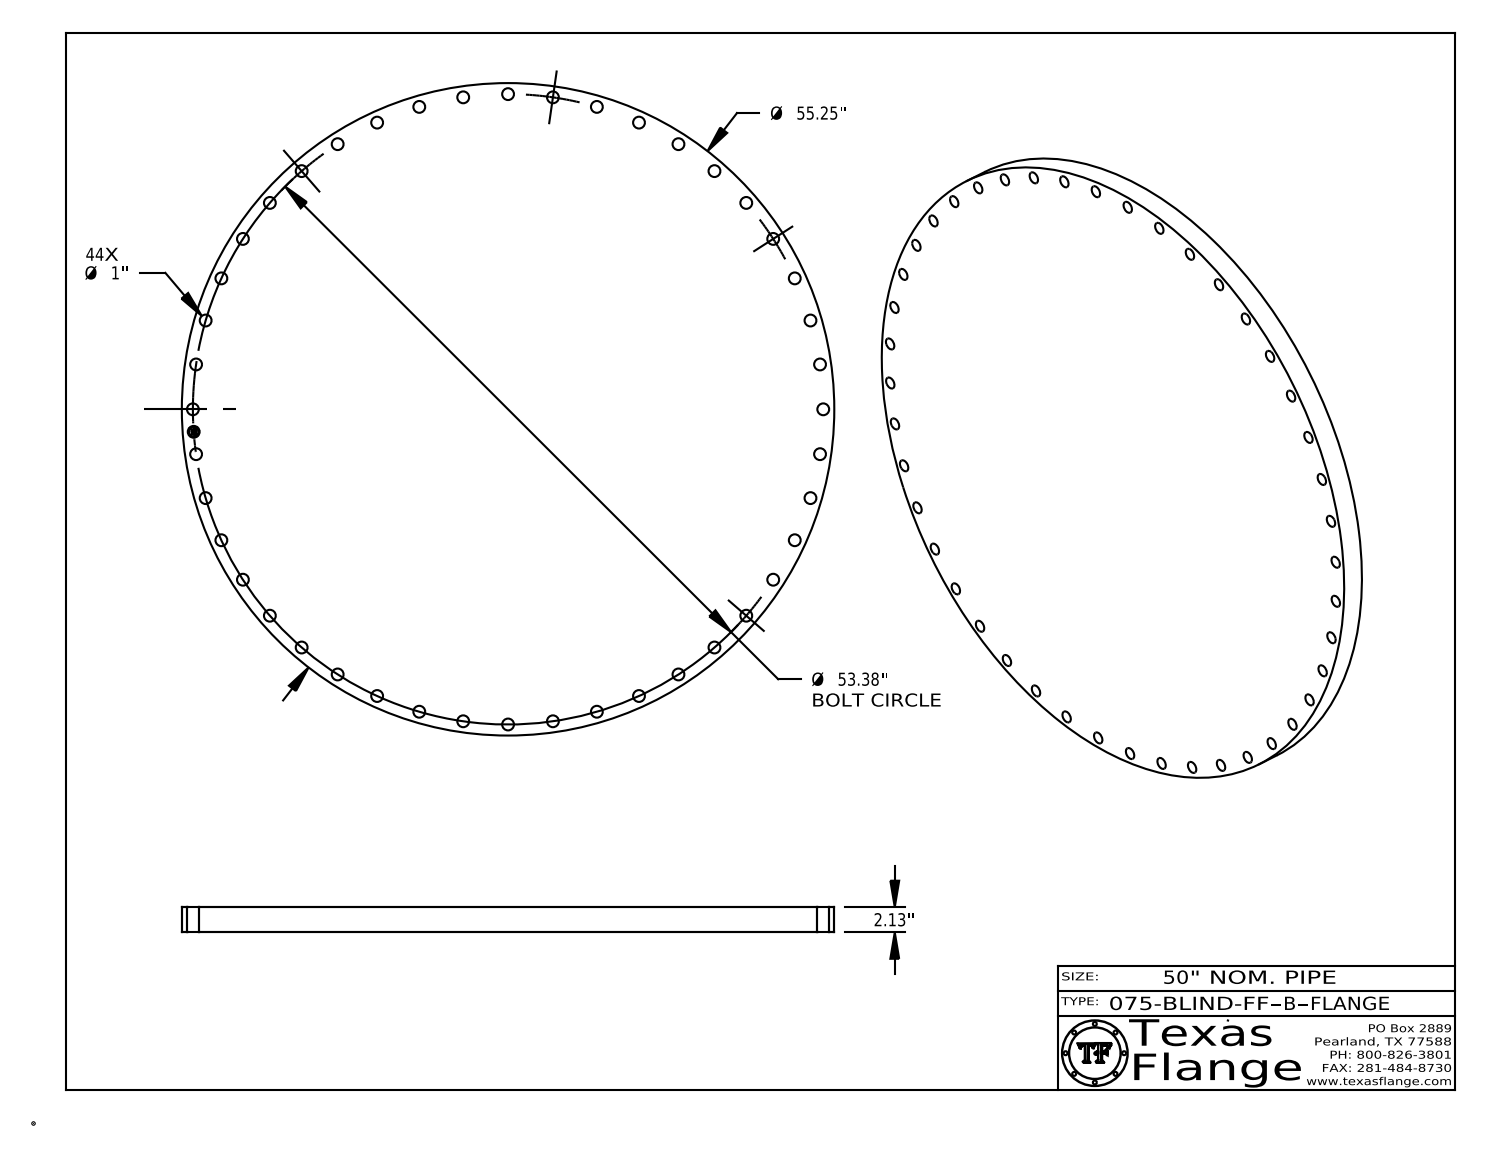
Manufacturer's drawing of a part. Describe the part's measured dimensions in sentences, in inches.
The part is named "075-BLIND-FF, Series B". Its 3-D file was written by "CATIA V5 STEP AP214 (AUTOMOTIVE_DESIGN)". It is 1 solid with 477 faces: 367 planar, 110 cylindrical and 0 other. Overall it measures 55.25 by 55.25 by 2.13 inches. Its volume is 5 033 cubic inches and its surface area 5 390 square inches. Round holes: 45 of diameter 1. Round bosses or shafts: 8 of diameter 0.061, 1 of diameter 55.25, 1 of diameter 0.788. The main face-to-face distances are 2.13, 0.015, 2.115, 0.298, 0.292, 0.054, 0.193, 0.248, 0.044, 0.15. The hole center spacings are 7.597, 52.837, 15.039, 51.218, 3.808, 42.733, 44.906, 50.015.
